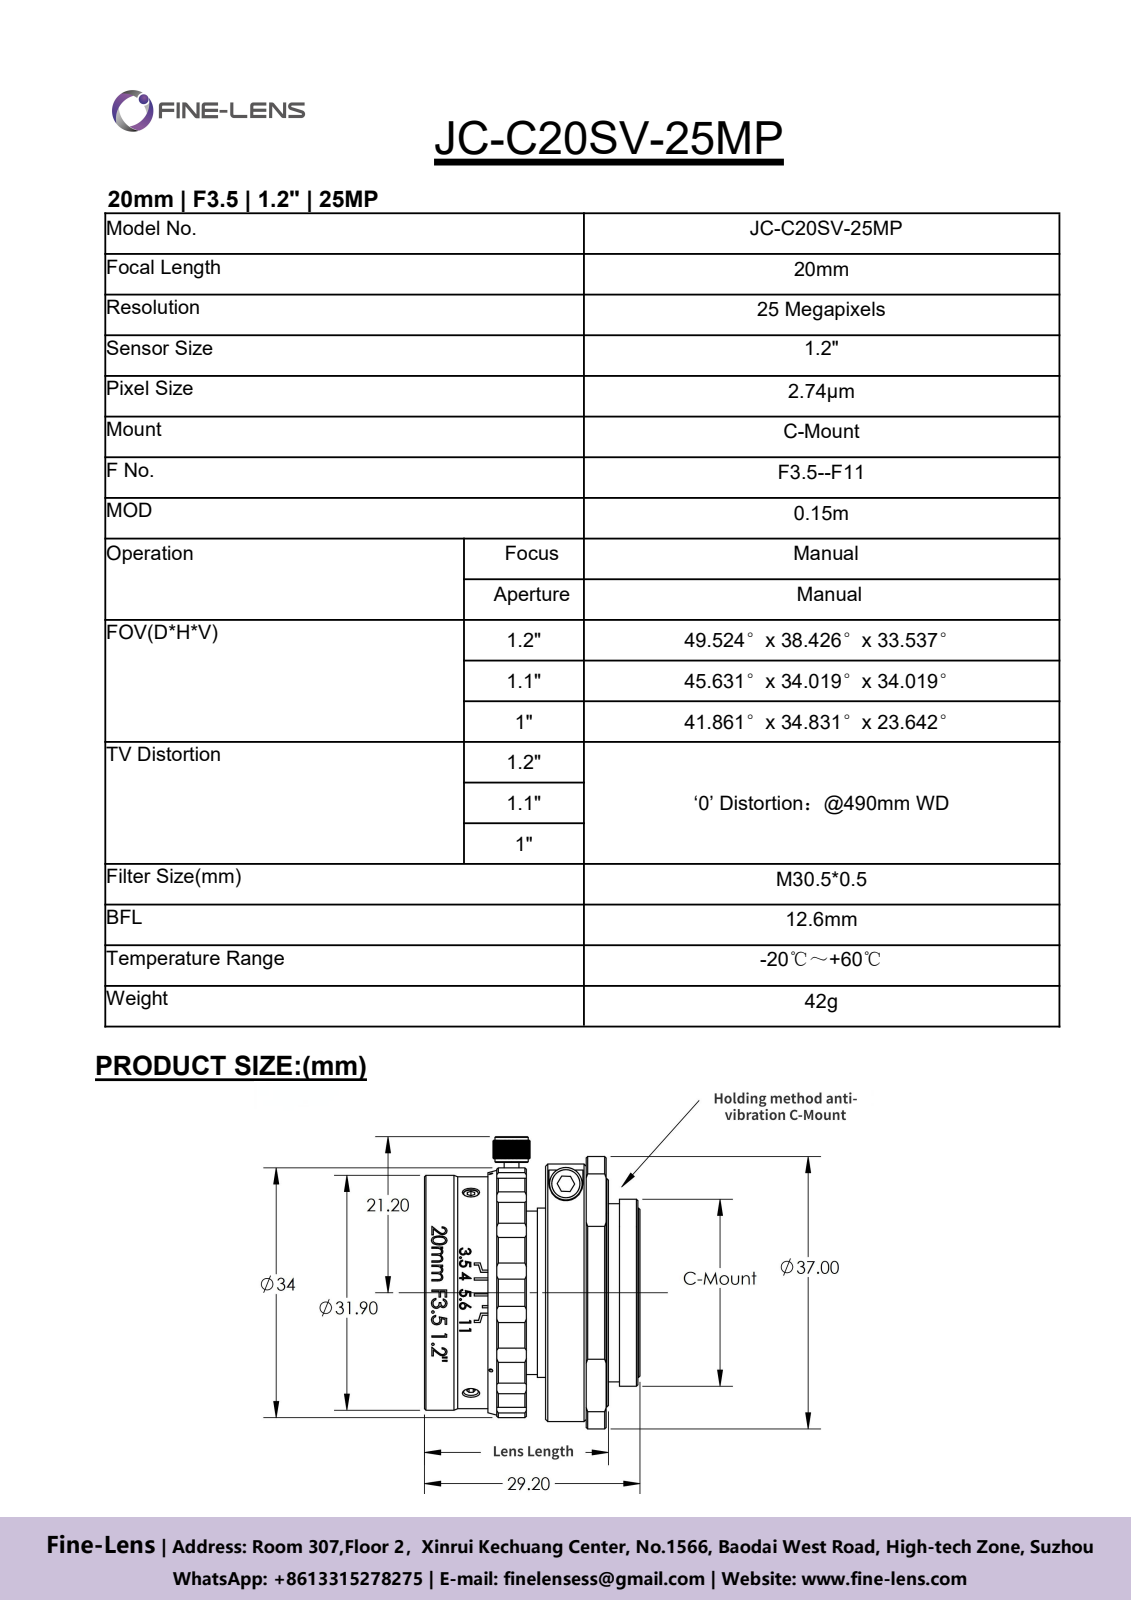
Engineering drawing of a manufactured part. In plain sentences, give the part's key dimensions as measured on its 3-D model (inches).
The part is named "1.2 20mm; M2.5x2.5 平头顶丝". Its 3-D file was written by "SolidWorks 2018 (AUTOMOTIVE_DESIGN)". It is 11 solids with 1327 faces: 475 planar, 291 cylindrical and 561 other. Overall it measures 1.563 by 1.457 by 1.15 inches. Its volume is 1.2 cubic inches and its surface area 20.37 square inches. Round holes: 4 of diameter 0.079, 3 of diameter 0.02, 1 of diameter 0.063, 1 of diameter 0.106, 1 of diameter 0.882, 1 of diameter 0.913, 1 of diameter 0.945, 1 of diameter 1.024, 1 of diameter 1.039, 1 of diameter 1.063, 1 of diameter 1.181, 1 of diameter 1.209. Round bosses or shafts: 4 of diameter 0.098, 1 of diameter 1.378, 1 of diameter 1.256, 1 of diameter 1.24, 1 of diameter 1.22, 1 of diameter 1.177, 1 of diameter 1.031, 1 of diameter 1. Partial cylindrical surfaces (rounded edges, fillets, slot ends): 19 of radius 0.098, 1 of radius 0.069, 1 of radius 0.091, 1 of radius 0.157, 1 of radius 0.62, 1 of radius 0.628, 1 of radius 0.669, 1 of radius 0.728. The main face-to-face distances are 0.679, 0.217, 0.37, 0.309, 0.462, 0.092, 0.976, 0.606, 0.514, 0.298. The hole center spacings are 0.217.
